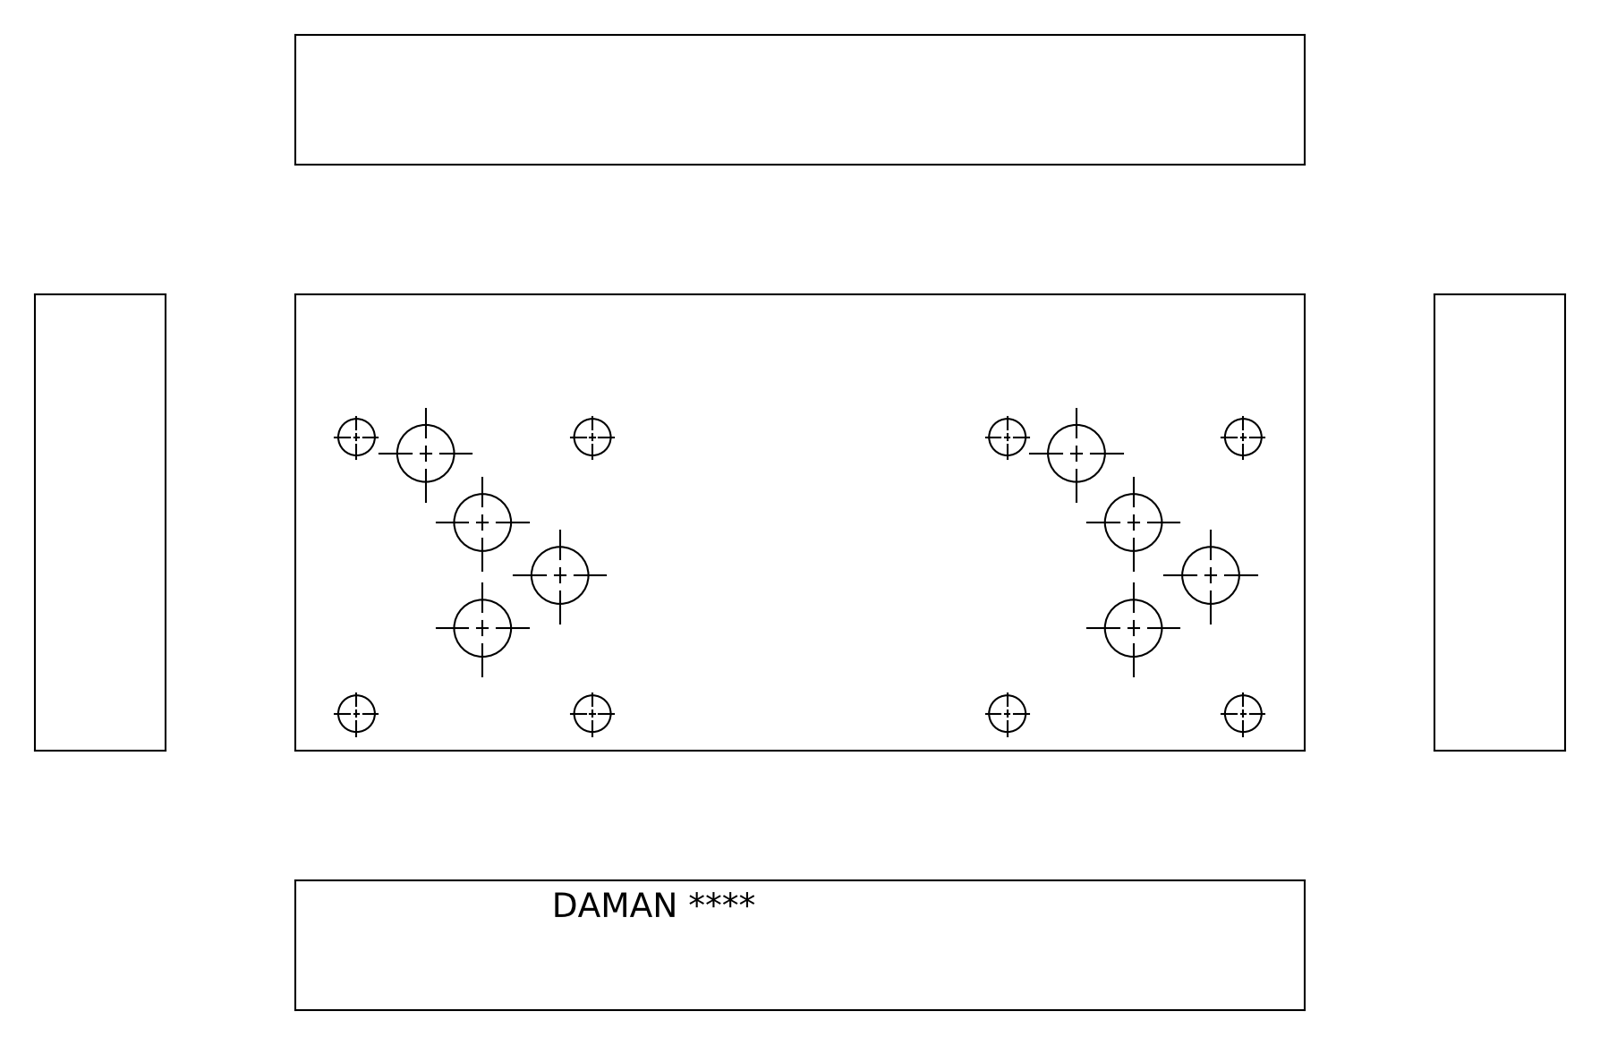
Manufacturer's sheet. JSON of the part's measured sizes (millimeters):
{"part_name": "Part_AD05TP025AB_3D", "step_written_by": "Autodesk Inventor 2021 (AUTOMOTIVE_DESIGN)", "units": "millimeters", "bodies": {"solids": 1, "faces": 399, "planar": 250, "cylindrical": 34, "other": 115}, "overall_size": [196.85, 88.9, 25.4], "volume_mm3": 415021, "surface_area_mm2": 59291, "round_holes": [[11.13, 14], [15.88, 10], [7.14, 8], [11.11, 2]], "face_to_face_distances": [25.4, 88.9, 196.85, 1.32, 24.08, 88.86, 0.64, 3.62, 10.48, 9.16], "hole_center_spacings": [18.28, 17.49, 126.98, 126.99, 27.7, 35.42, 47.63, 52.57]}
